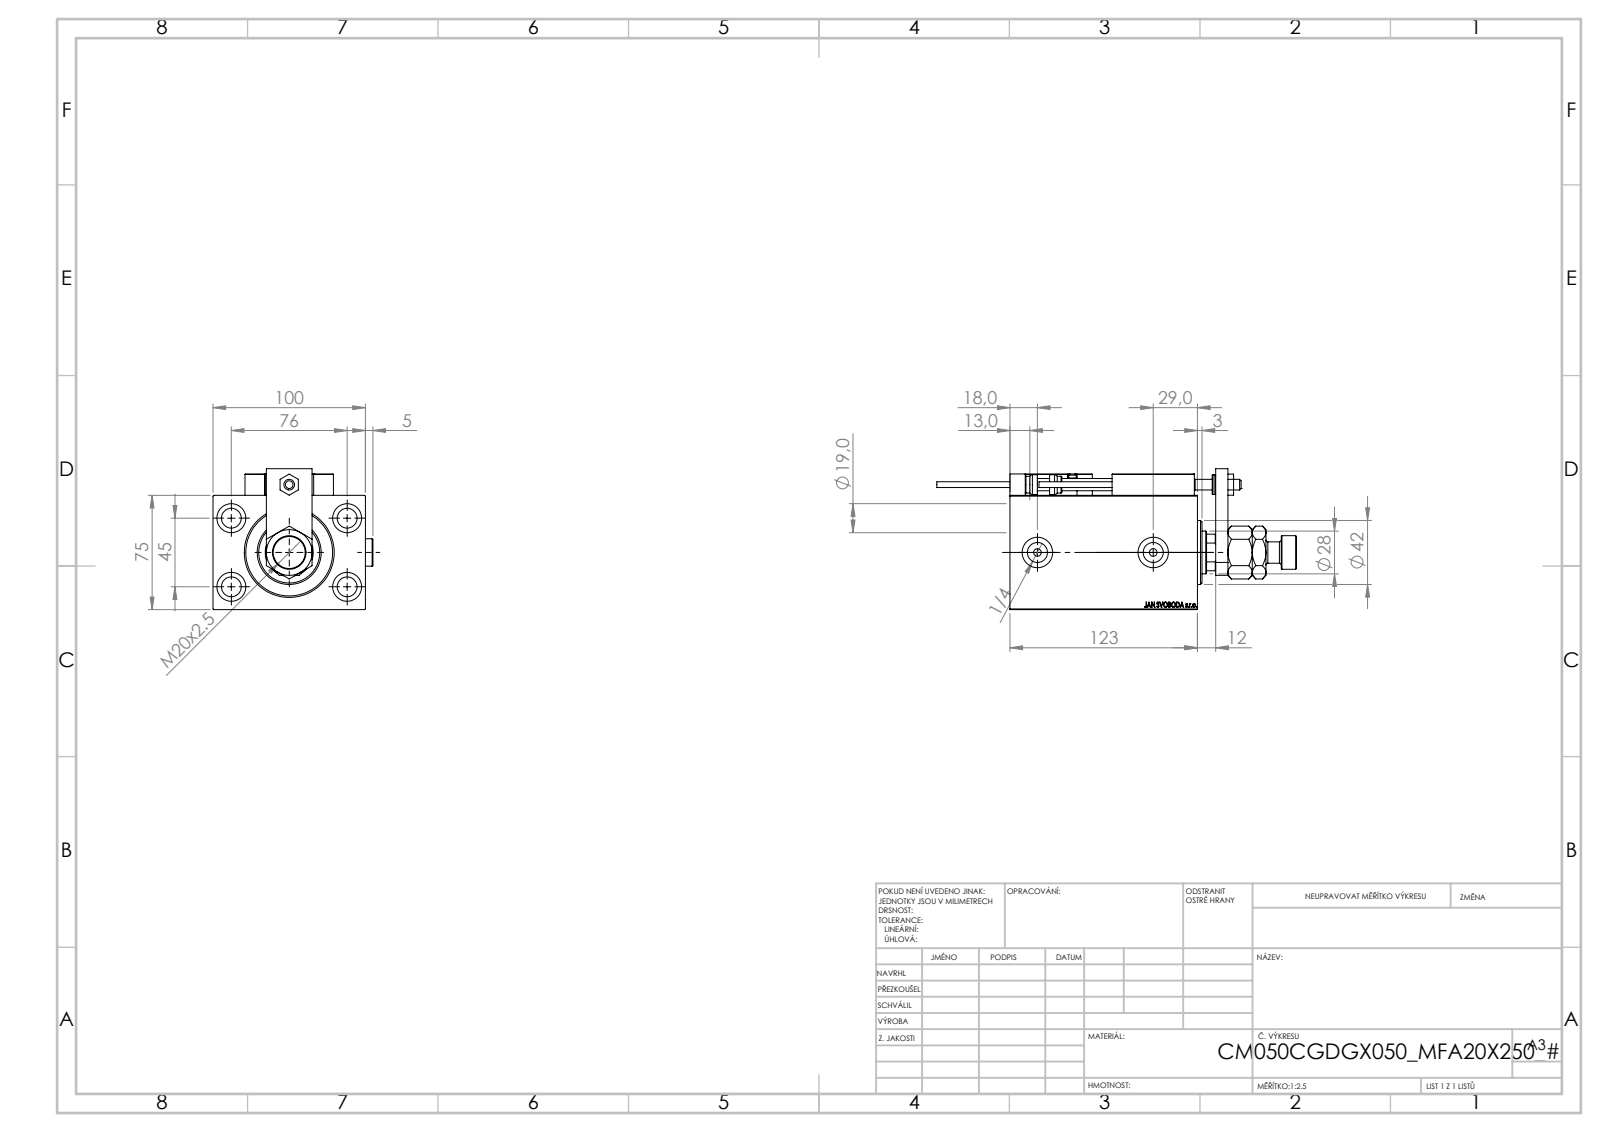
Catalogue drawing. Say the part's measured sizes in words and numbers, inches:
The part is named "V450CM_VC_B; NUT_D12; Block; X_Y_MFA (+8 more)". Its 3-D file was written by "SolidWorks 2019 (CONFIG_CONTROL_DESIGN)". It is 26 solids with 1391 faces: 611 planar, 210 cylindrical and 570 other. Overall it measures 9.291 by 4.13 by 3.642 inches. Its volume is 51.94 cubic inches and its surface area 248.6 square inches. Round holes: 5 of diameter 0.315, 4 of diameter 0.126, 4 of diameter 0.157, 4 of diameter 0.197, 4 of diameter 0.512, 4 of diameter 0.748, 3 of diameter 0.787, 2 of diameter 0.518, 1 of diameter 0.276, 1 of diameter 0.728, 1 of diameter 1.102, 1 of diameter 1.24. Round bosses or shafts: 2 of diameter 0.709, 2 of diameter 0.197, 2 of diameter 0.15, 1 of diameter 1.654, 1 of diameter 0.866, 1 of diameter 0.551, 1 of diameter 0.512, 1 of diameter 0.433. Partial cylindrical surfaces (rounded edges, fillets, slot ends): 30 of radius 0.012, 2 of radius 0.118, 1 of radius 0.531. The main face-to-face distances are 2.953, 3.937, 0.551, 4.843, 0.472, 4.291, 0.787, 0.315, 0.945, 0.984. The hole center spacings are 1.739, 2.992, 0.448, 0.787, 1.165, 1.169, 1.42, 1.661.
